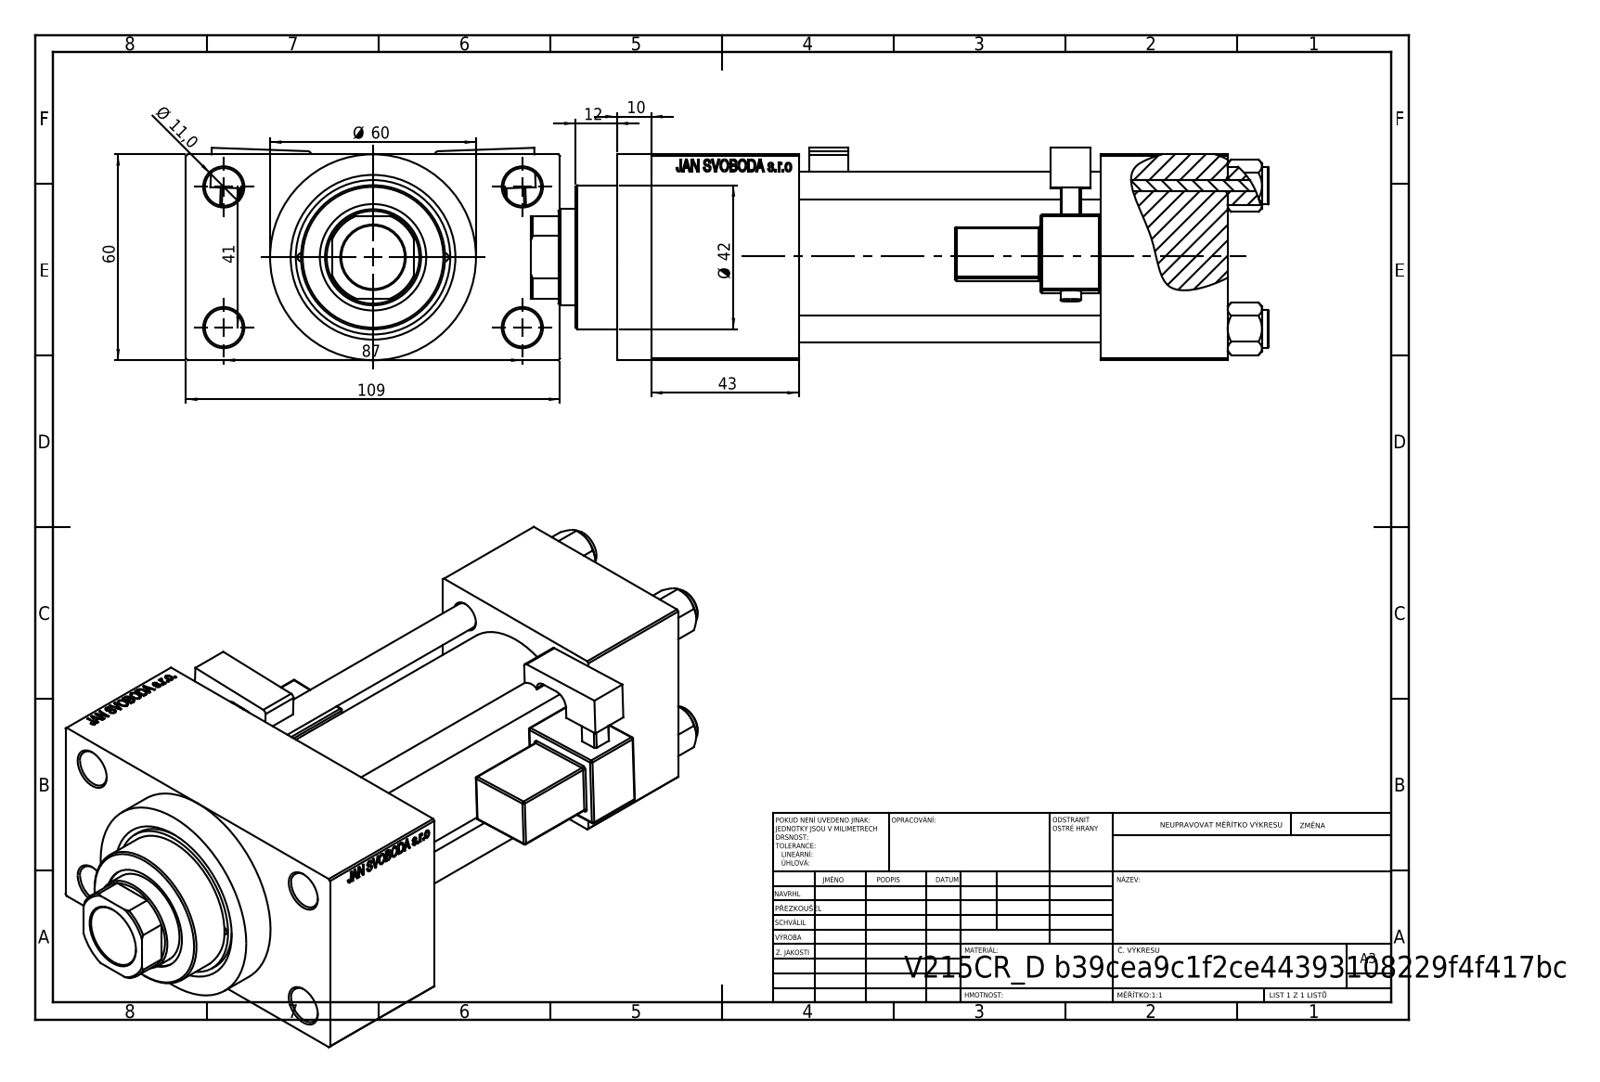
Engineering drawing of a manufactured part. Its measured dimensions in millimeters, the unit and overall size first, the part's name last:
Units: millimetres
Overall size (bounding box): 215 × 109 × 61.9
Round holes (diameter × count): ⌀8 ×4, ⌀11 ×4, ⌀2.5 ×2, ⌀7 ×2, ⌀16.66 ×2, ⌀24 ×2, ⌀18.5 ×1, ⌀28 ×1, ⌀31 ×1, ⌀40 ×1, ⌀45 ×1
Round bosses / shafts (diameter × count): ⌀11 ×4, ⌀6 ×2, ⌀60 ×1, ⌀46 ×1, ⌀42 ×1
Partial cylindrical surfaces — rounded edges, fillets, slot ends (radius × count): R0.5 ×48, R1 ×2, R2.5 ×2, R4 ×2, R13.5 ×1
Main face-to-face distances: 60, 88, 24.5, 84.5, 37, 125, 168, 131, 43, 109
Hole centre spacings: 20.85, 22.65, 29.49, 30.62, 41.7, 46.53, 47.15, 48.09
Volume: 606 164 mm³ · Surface area: 154 923 mm²
Bodies: 13 solids, 1268 faces (560 planar, 152 cylindrical, 556 other)
Part name (STEP PRODUCT): V215_VC_A; V215CR_MSU; NUT_M5_D; V215CR_D_Body (+2 more)
STEP written by: SolidWorks 2019 (CONFIG_CONTROL_DESIGN)
